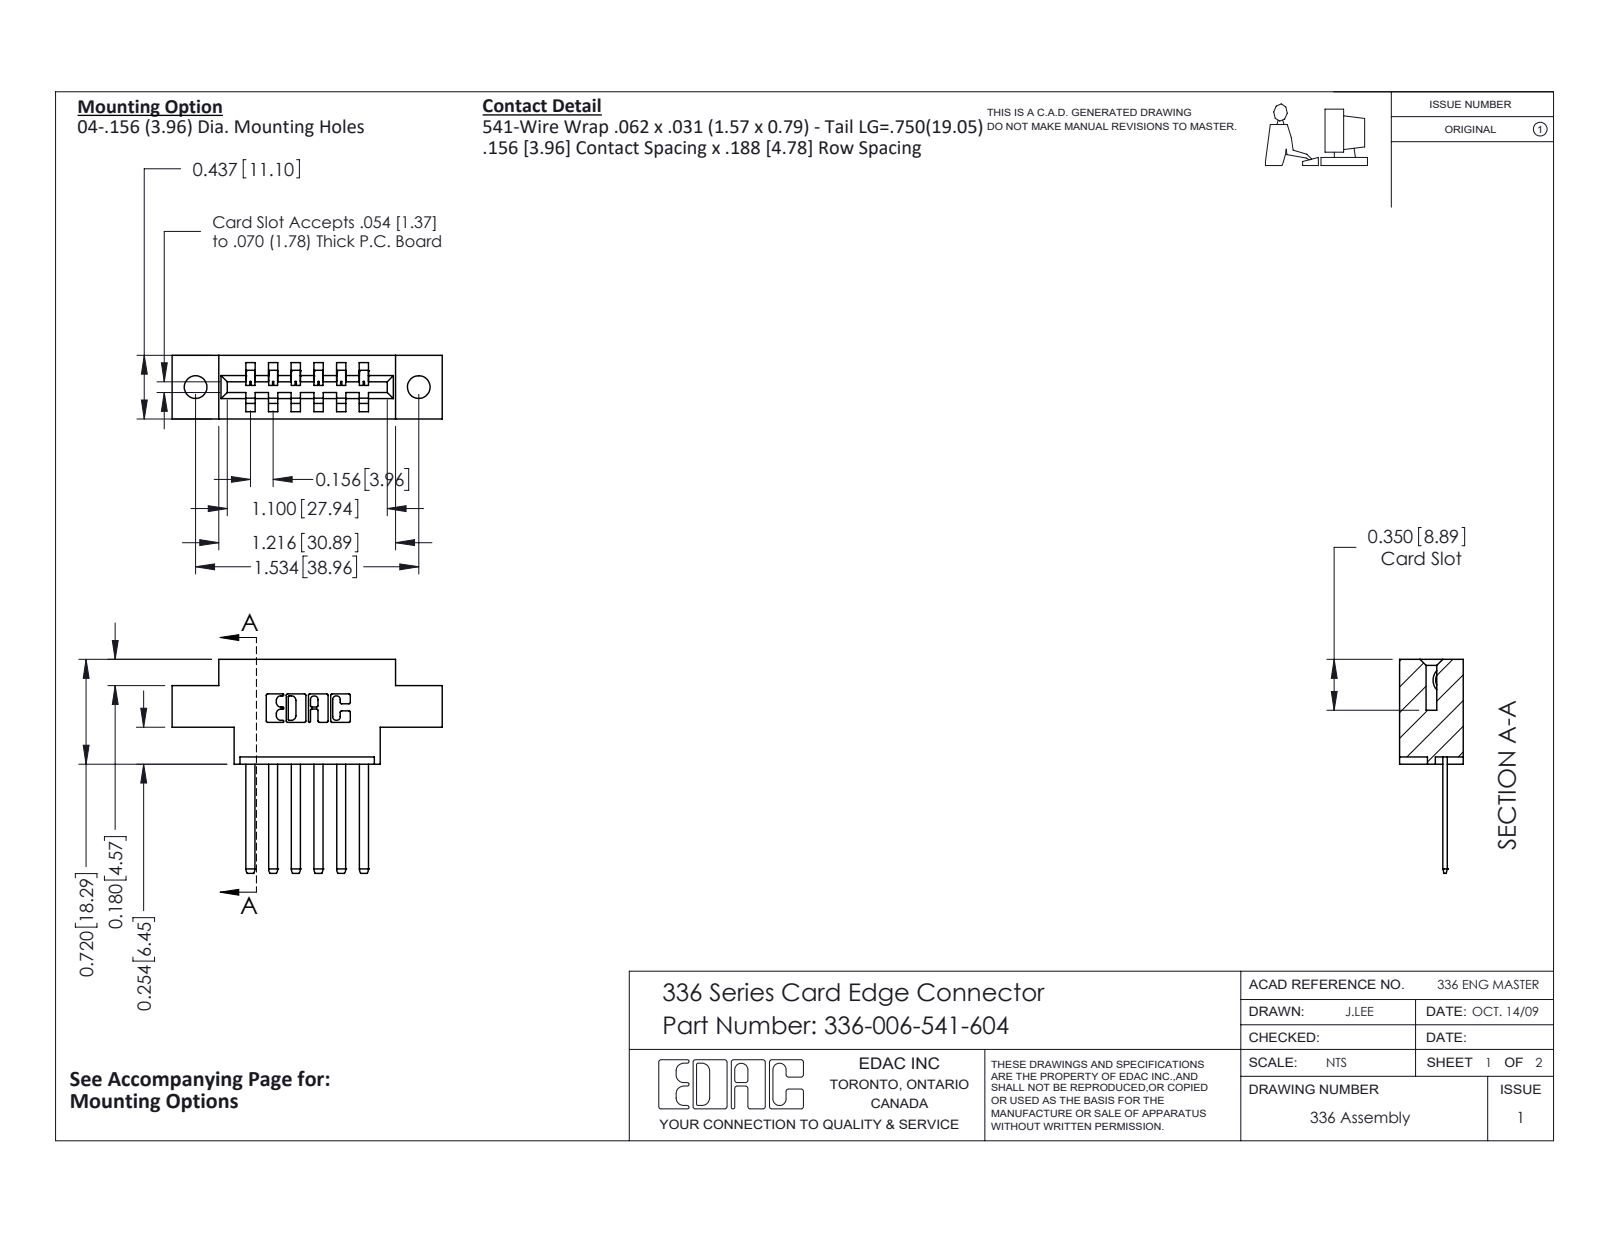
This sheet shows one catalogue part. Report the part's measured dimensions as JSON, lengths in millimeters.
{"part_name": "336-006-541-604; 336 Part_Offset - .156 Dia - TH; 336-290-001_336-290-541", "step_written_by": "SolidWorks 2020 (CONFIG_CONTROL_DESIGN)", "units": "millimeters", "bodies": {"solids": 7, "faces": 418, "planar": 278, "cylindrical": 140, "other": 0}, "overall_size": [47.2, 37.3, 11.1], "volume_mm3": 5750, "surface_area_mm2": 5672, "round_holes": [[4, 2]], "partial_cylinders_radius": [[0.3, 22], [0.1, 12], [1.4, 12], [0.2, 6], [0.8, 6], [0.7, 3], [0.6, 2], [1, 2]], "face_to_face_distances": [4, 11.1, 7.9, 9.6, 5.6, 4.6, 6.5, 8.3, 3.6, 7.5], "hole_center_spacings": [39]}
